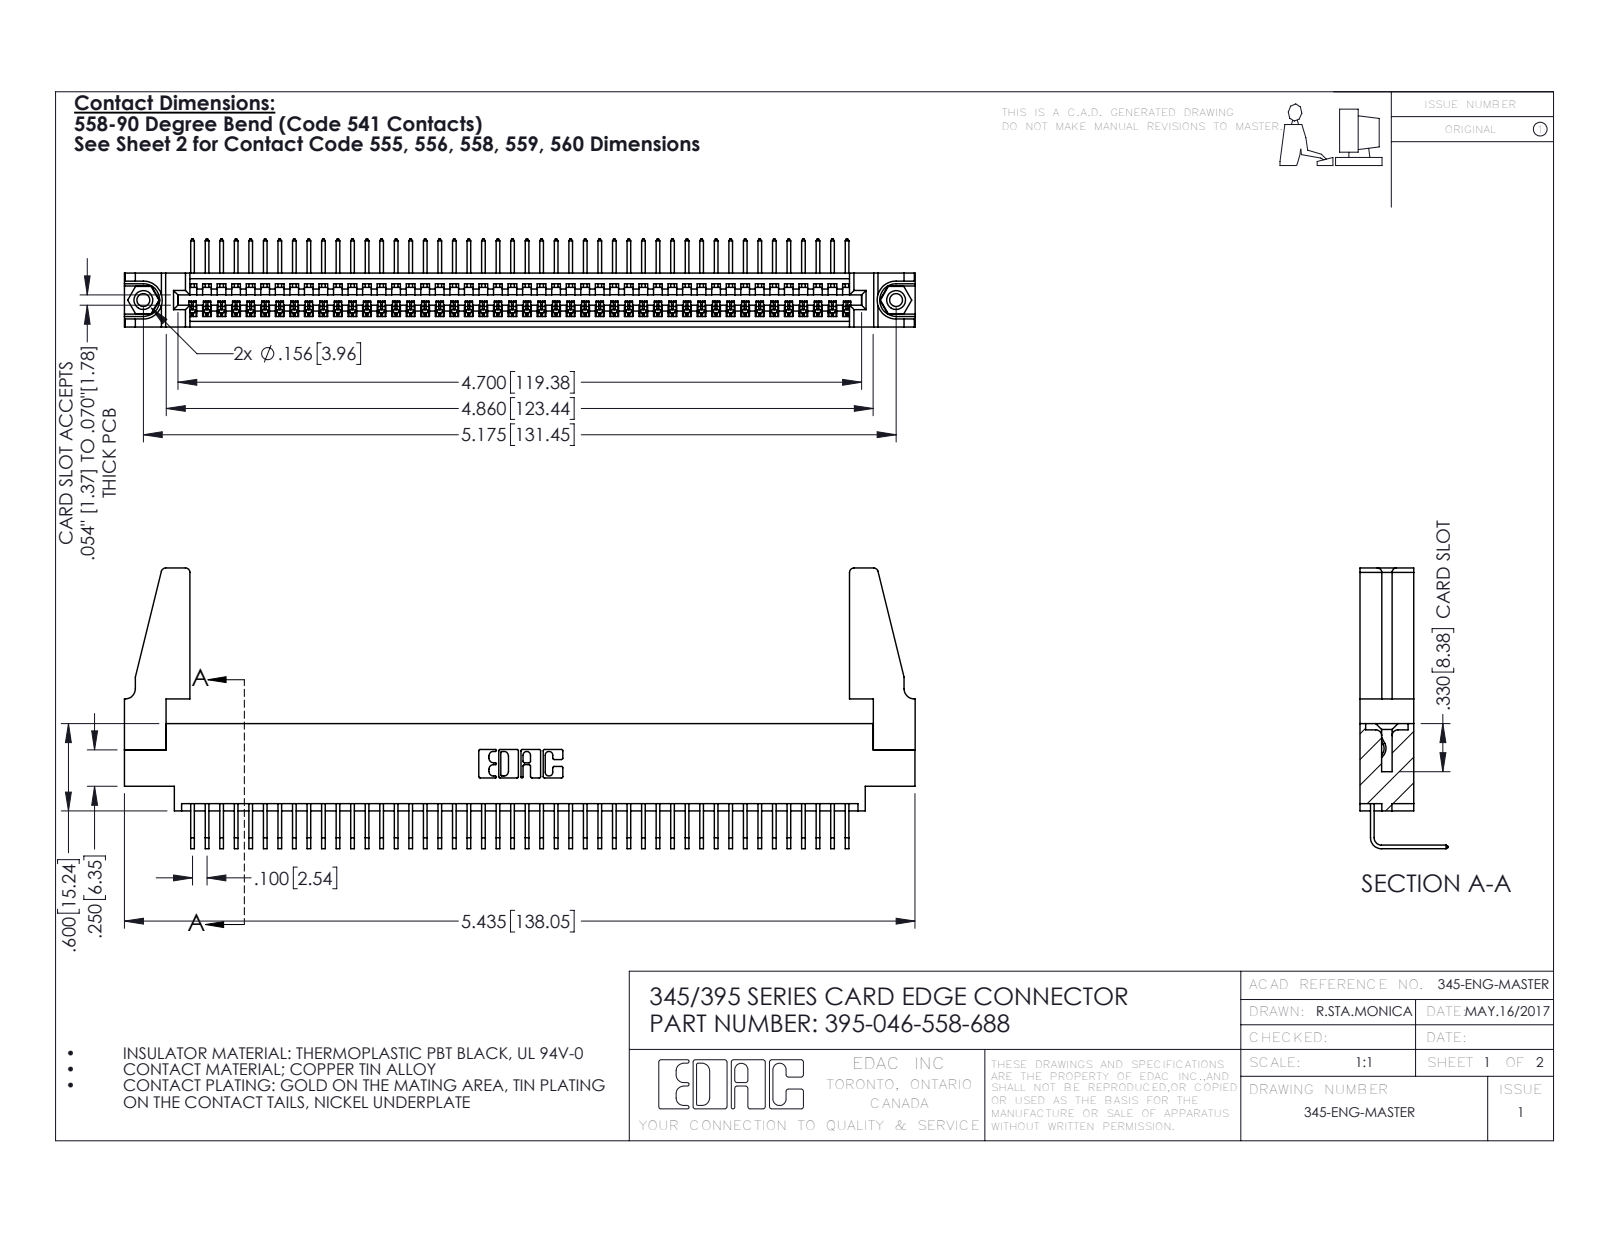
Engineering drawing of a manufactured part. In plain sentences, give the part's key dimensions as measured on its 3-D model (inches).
The part is named "345 Part_0.170 Offset - 0.156 Dia-TH; 345-292-001_558 Tail - 2; 345-250-001_345-250-001-102; 345-220-078_345-220-088 (+1 more)". Its 3-D file was written by "SolidWorks 2016 (CONFIG_CONTROL_DESIGN)". It is 51 solids with 3014 faces: 2088 planar, 910 cylindrical and 16 other. Overall it measures 5.436 by 1.929 by 0.605 inches. Its volume is 1.003 cubic inches and its surface area 33.69 square inches. Round holes: 2 of diameter 0.089, 2 of diameter 0.125, 2 of diameter 0.156, 1 of diameter 0.064. Round bosses or shafts: 2 of diameter 0.155. Partial cylindrical surfaces (rounded edges, fillets, slot ends): 92 of radius 0.006, 22 of radius 0.01, 8 of radius 0.03, 6 of radius 0.007, 6 of radius 0.031, 3 of radius 0.026, 2 of radius 0.031, 2 of radius 0.04. The main face-to-face distances are 0.072, 0.37, 0.298, 0.2, 0.098, 0.272, 0.025, 0.225, 0.175, 0.149. The hole center spacings are 0.27, 4.939, 5.175.
